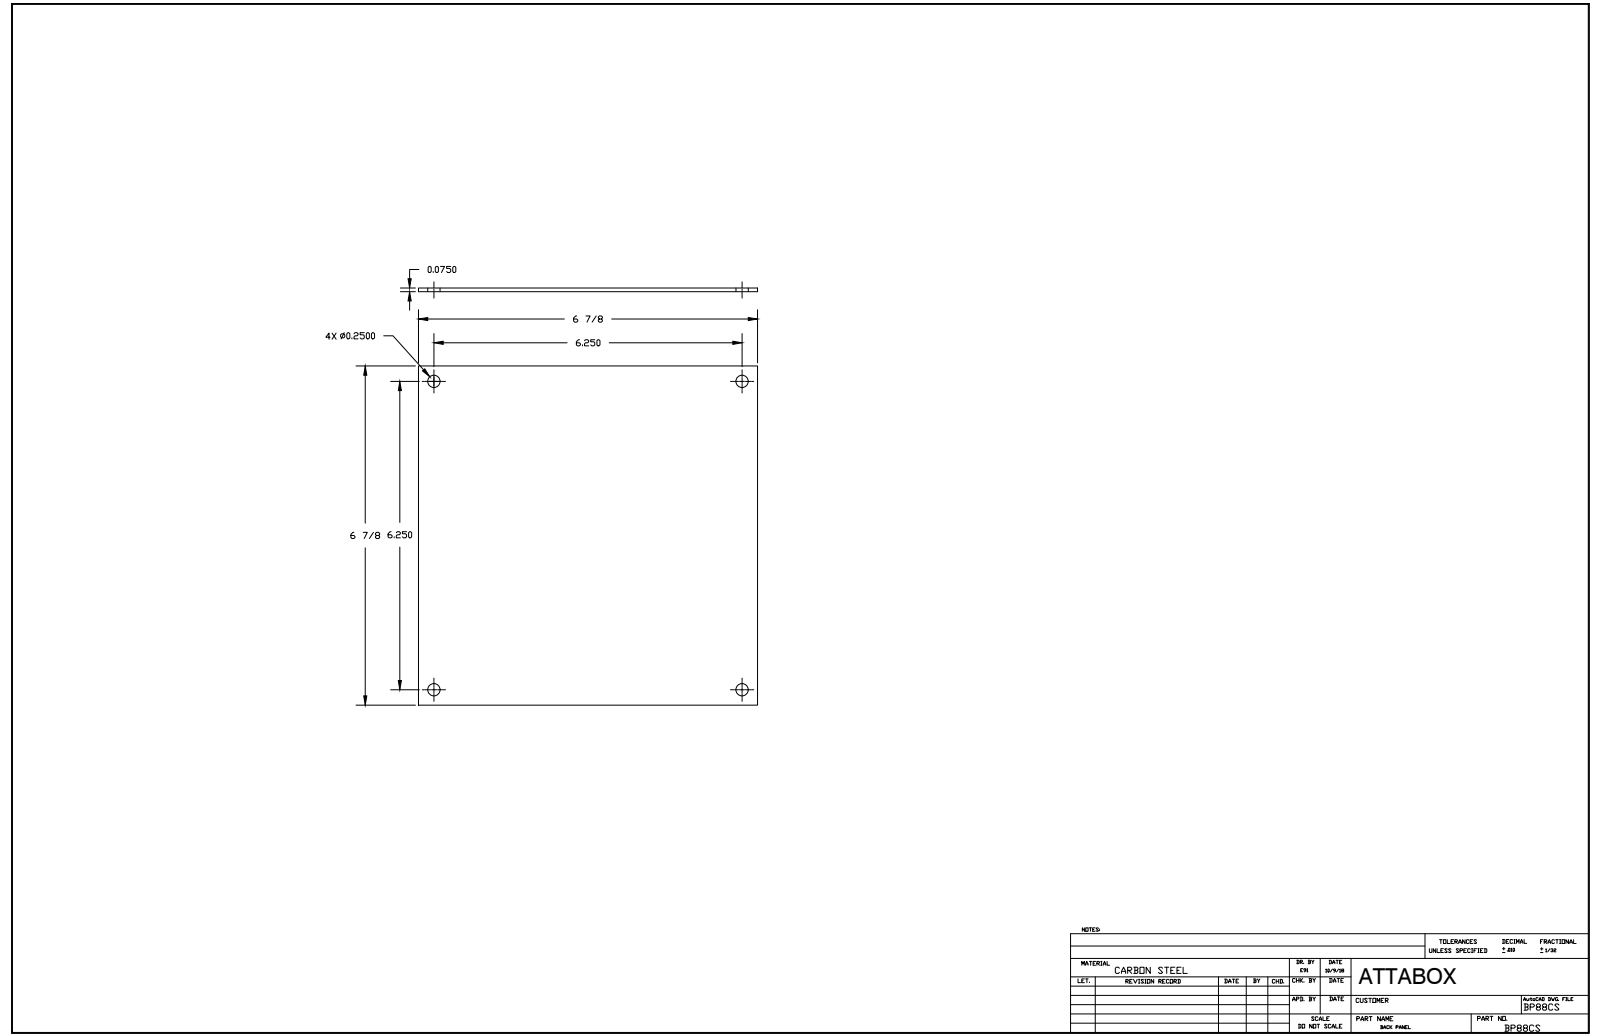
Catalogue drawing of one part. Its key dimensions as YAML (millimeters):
part_name: "BP88CS_STP"
step_written_by: "Autodesk Inventor 2014 (AUTOMOTIVE_DESIGN)"
units: millimeters
bodies: {solids: 1, faces: 10, planar: 6, cylindrical: 4, other: 0}
overall_size: [174.62, 174.62, 1.91]
volume: 57850
surface_area: 62217
round_holes:
  - {diameter: 6.35, count: 4}
face_to_face_distances: [1.9, 174.62]
hole_center_spacings: [158.76, 224.52]
